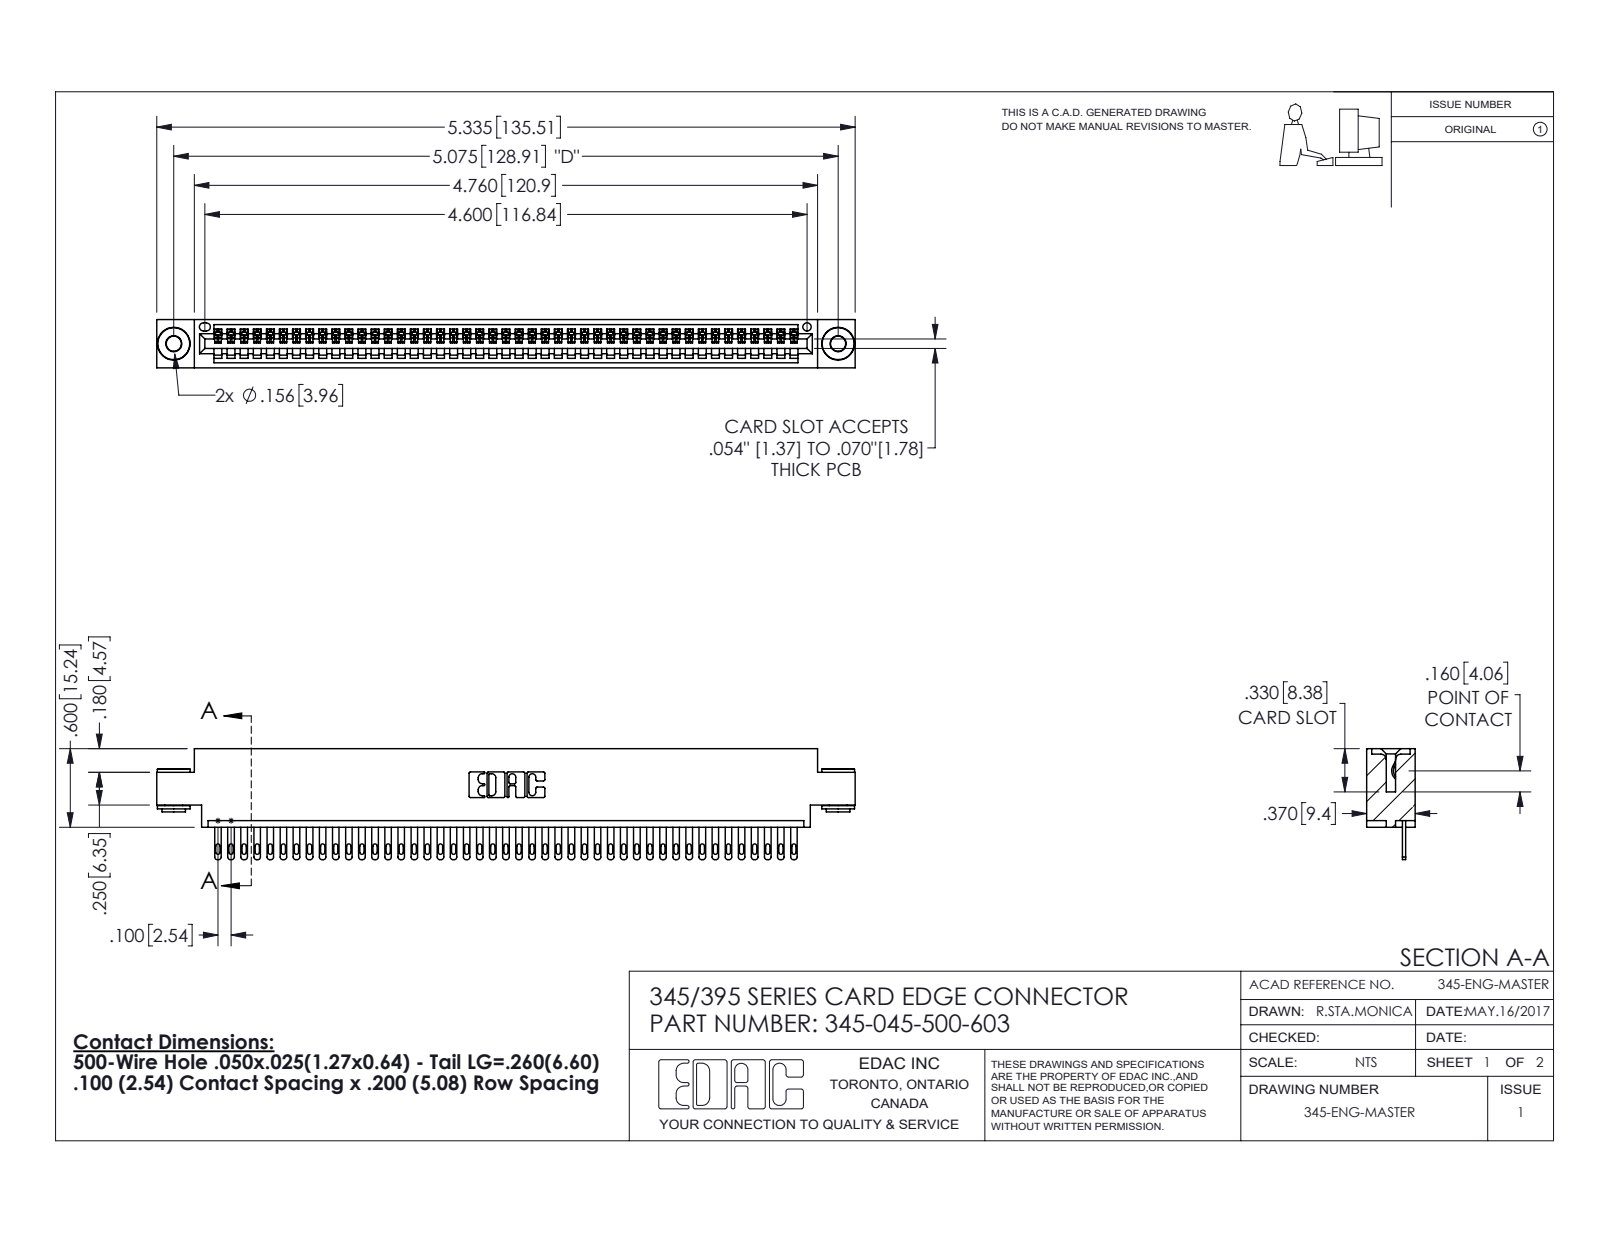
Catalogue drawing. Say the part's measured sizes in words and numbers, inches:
The part is named "345-045-500-603; 345 Part_0.170 Offset - 0.156 Dia-TH; 345-250-002_345-250-002-102; 345-292-001_345-293-100". Its 3-D file was written by "SolidWorks 2016 (CONFIG_CONTROL_DESIGN)". It is 48 solids with 2598 faces: 1624 planar, 966 cylindrical and 8 other. Overall it measures 5.335 by 0.847 by 0.37 inches. Its volume is 0.783 cubic inches and its surface area 27.17 square inches. Round holes: 2 of diameter 0.116, 2 of diameter 0.156, 1 of diameter 0.064. Round bosses or shafts: 2 of diameter 0.25, 2 of diameter 0.18, 2 of diameter 0.136. Partial cylindrical surfaces (rounded edges, fillets, slot ends): 90 of radius 0.006, 90 of radius 0.016, 90 of radius 0.02, 22 of radius 0.01, 6 of radius 0.007, 6 of radius 0.031, 3 of radius 0.026, 2 of radius 0.031. The main face-to-face distances are 0.072, 0.298, 0.37, 0.098, 0.272, 0.025, 0.2, 0.225, 0.175, 0.149. The hole center spacings are 0.27, 4.839, 5.075.
